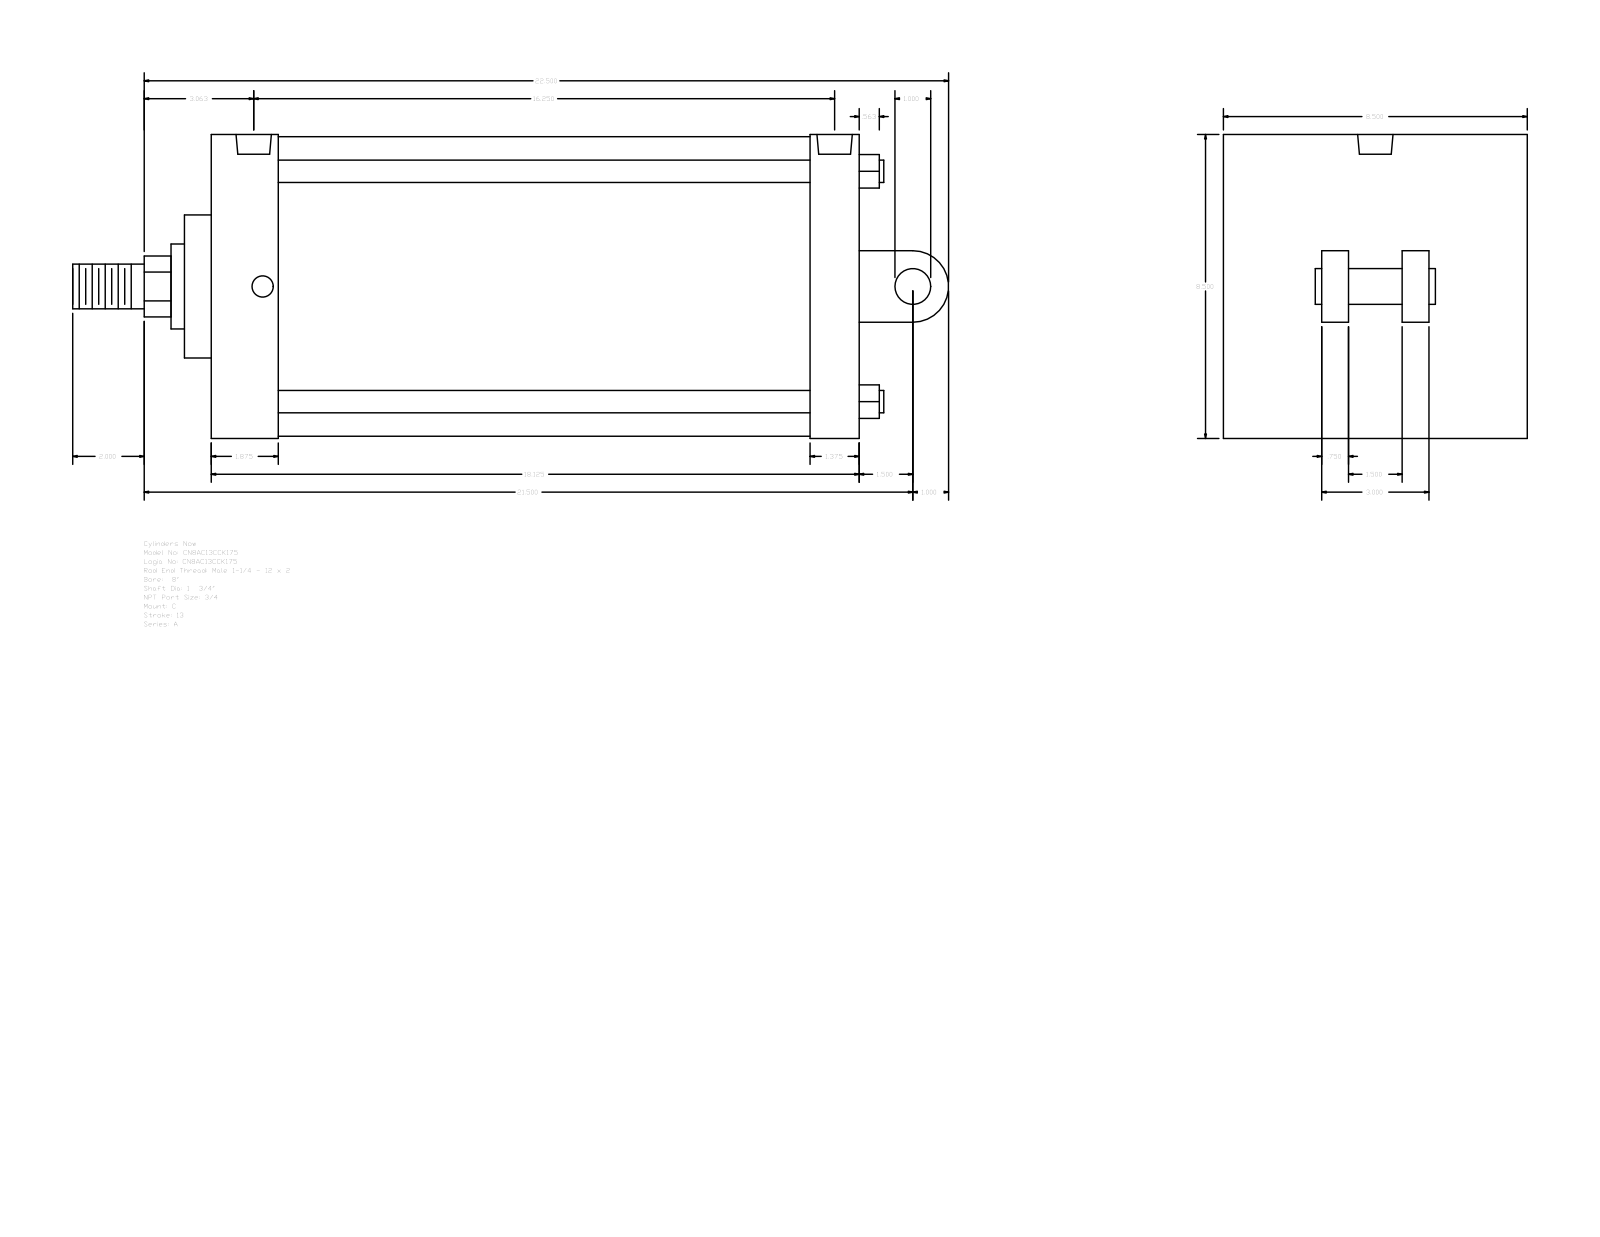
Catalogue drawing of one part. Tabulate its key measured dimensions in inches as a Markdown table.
| quantity | value |
| --- | --- |
| part name | A_C__0800_1.75 |
| STEP written by | GSSL Pune (CONFIG_CONTROL_DESIGN) |
| units | inches |
| bodies | 0 solids, 104 faces (75 planar, 29 cylindrical, 0 other) |
| overall size | 24.5 × 8.5 × 8.5 |
| round holes (diameter × count) | 0.594 × 4, 0.989 × 2 |
| round bosses / shafts (diameter × count) | 0.625 × 4, 8.375 × 1, 2.375 × 1, 1.75 × 1, 1.25 × 1, 1 × 1 |
| partial cylindrical surfaces (radius × count) | 0.852 × 1, 1 × 1 |
| main face-to-face distances | 18.125, 8.5, 0.75, 2.25, 1.875, 16.25, 16.75, 14.875, 1.375, 2.75 |
| hole center spacings | 0.25, 15.75, 16, 16.25 |
